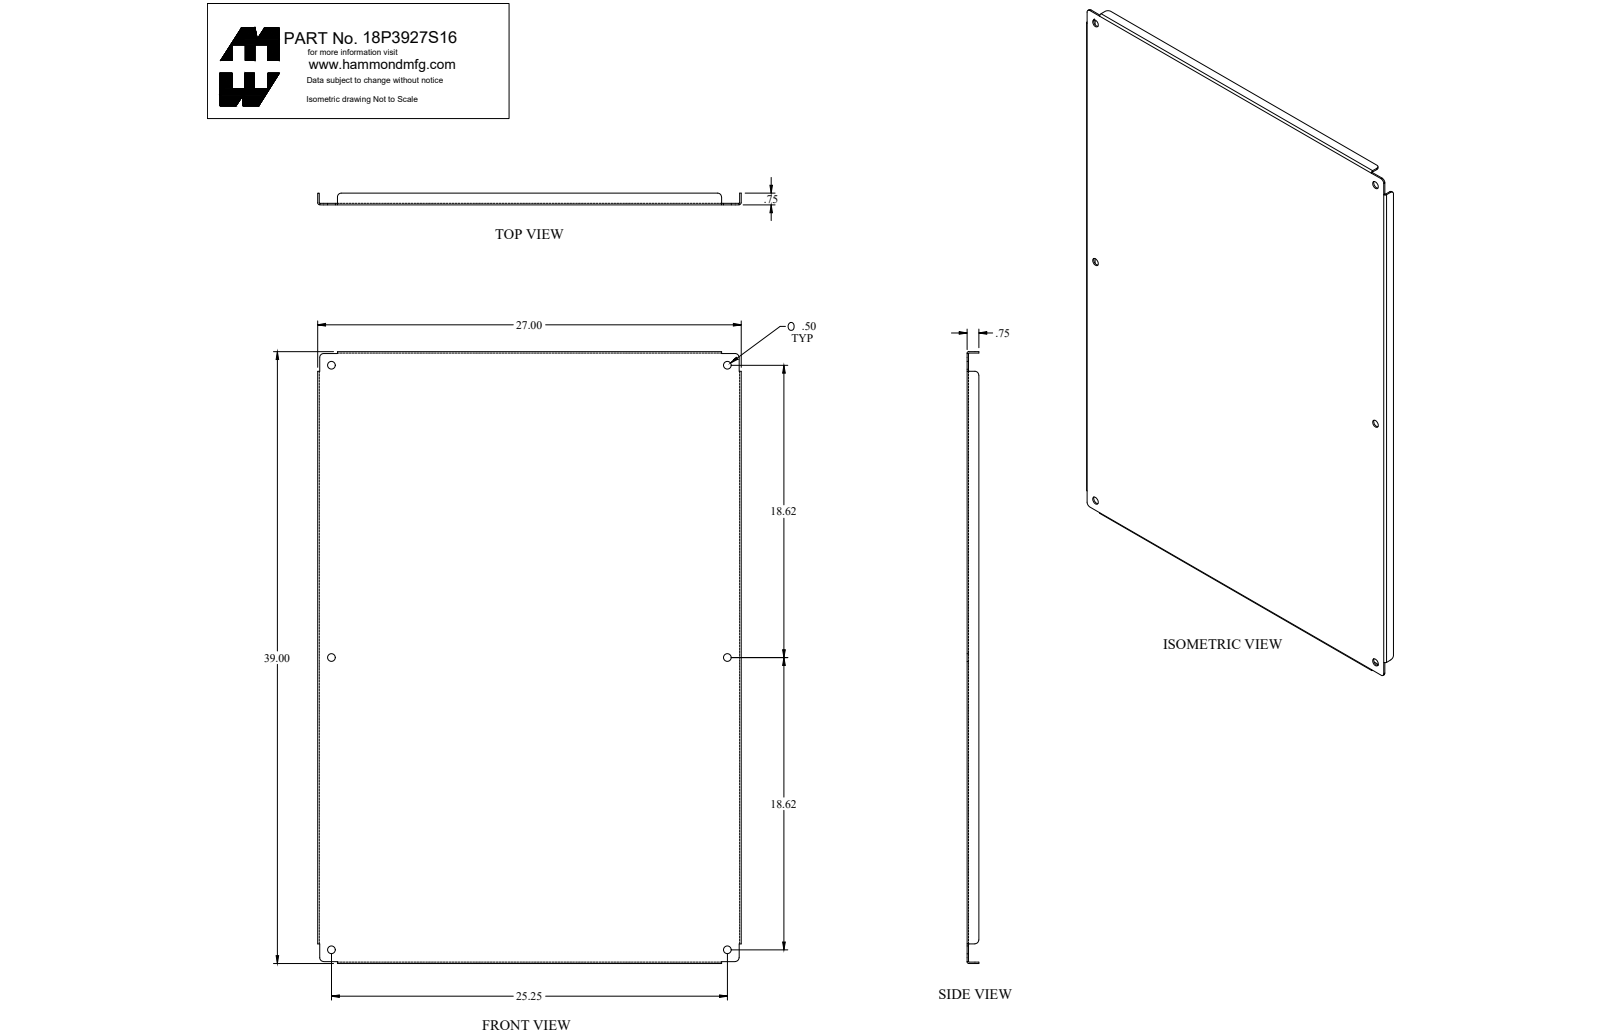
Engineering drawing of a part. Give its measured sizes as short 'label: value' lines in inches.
name: 18P3927S16_Default
written by: SolidWorks 2018 (CONFIG_CONTROL_DESIGN)
unit: in
bodies: 1 solid, 62 faces (30 planar, 32 cylindrical, 0 other)
size: 39 × 27 × 0.75
volume: 107 in³; area: 2 266 in²
holes: 6× ⌀0.5
rounds: 8× R0.25, 4× R0.03, 4× R0.125
face distances: 0.095, 26.905, 38.905, 27, 26.81, 39, 38.81, 0.75, 0.655, 0.125
hole spacings: 18.625, 31.376, 25.25, 37.25, 45.001
